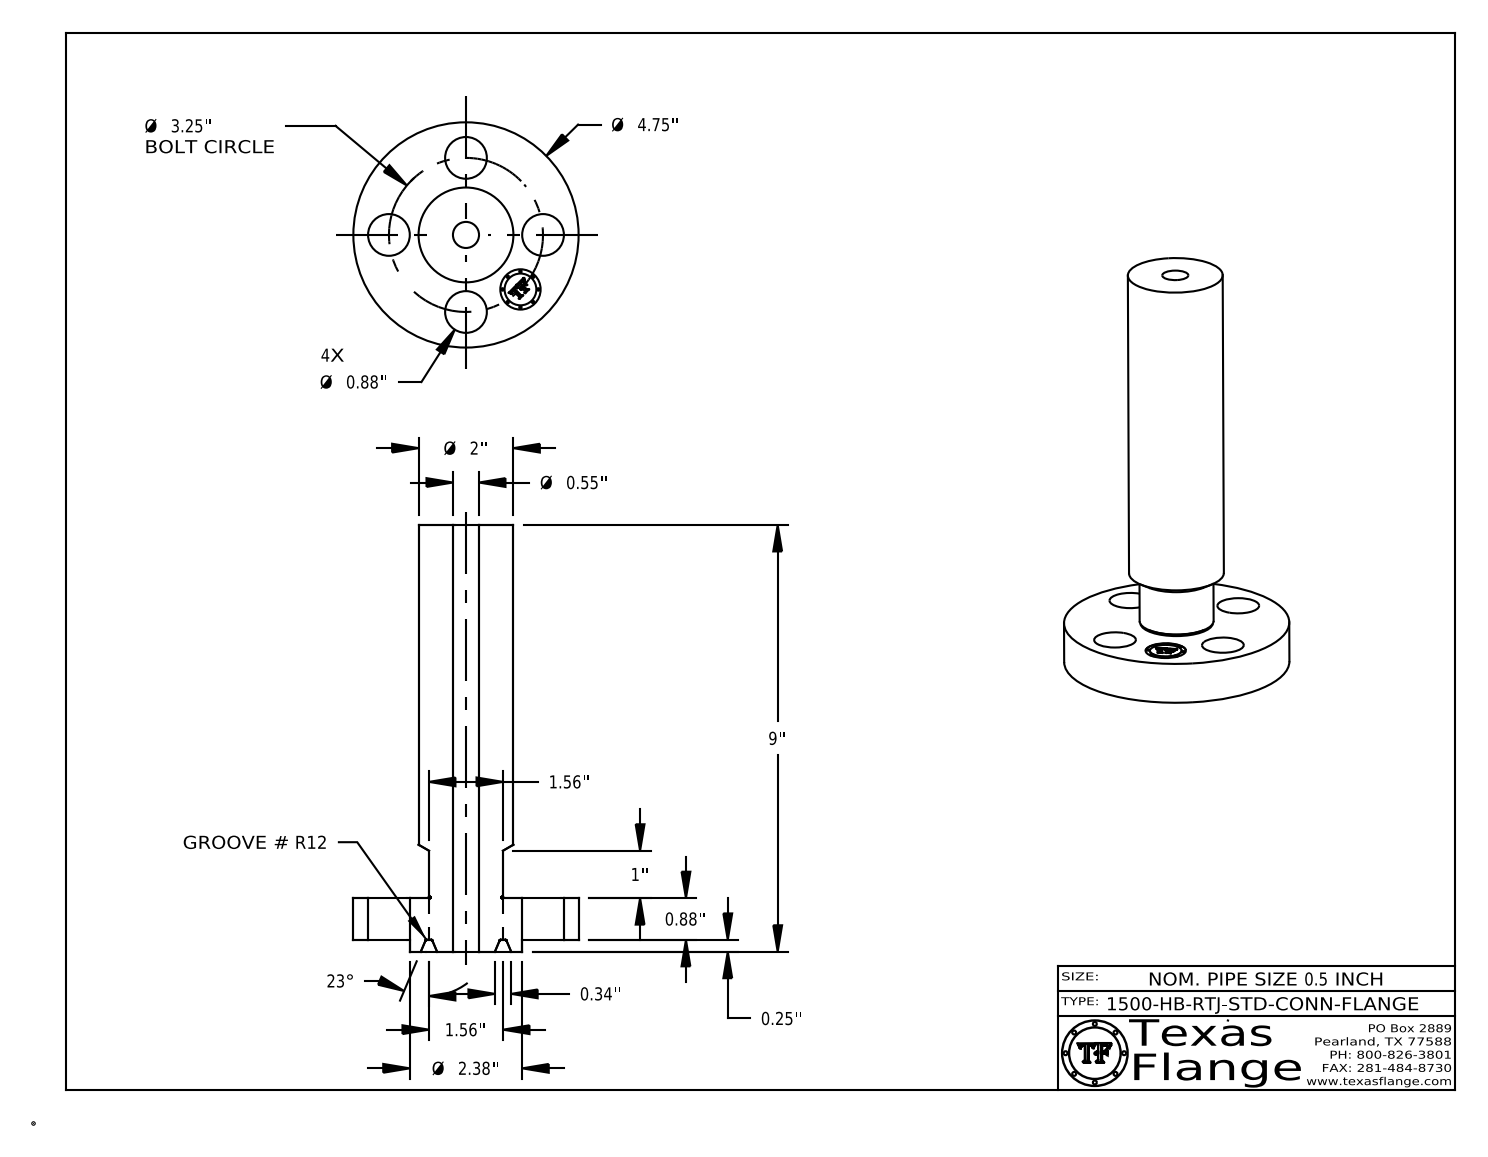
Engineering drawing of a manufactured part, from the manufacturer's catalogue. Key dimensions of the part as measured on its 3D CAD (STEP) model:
Part name (STEP PRODUCT): 0.5-1500-HB-RTJ-STD-CONN-FLANGE
STEP written by: CATIA V5 STEP AP214 (AUTOMOTIVE_DESIGN)
Units: inches
Bodies: 1 solid, 427 faces (371 planar, 42 cylindrical, 14 other)
Overall size (bounding box): 9 × 4.75 × 4.75
Volume: 35.54 in³ · Surface area: 122.1 in²
Round holes (diameter × count): ⌀0.88 ×4, ⌀0.55 ×1, ⌀0.85 ×1
Round bosses / shafts (diameter × count): ⌀0.051 ×8, ⌀4.75 ×1, ⌀2.375 ×1, ⌀2 ×1, ⌀1.56 ×1, ⌀0.67 ×1
Main face-to-face distances: 0.88, 8.75, 7.87, 0.25, 1.13, 9, 1.125, 0.875, 7.875, 0.254
Hole centre spacings: 1.625, 2.298, 1.244, 3.003, 3.25
